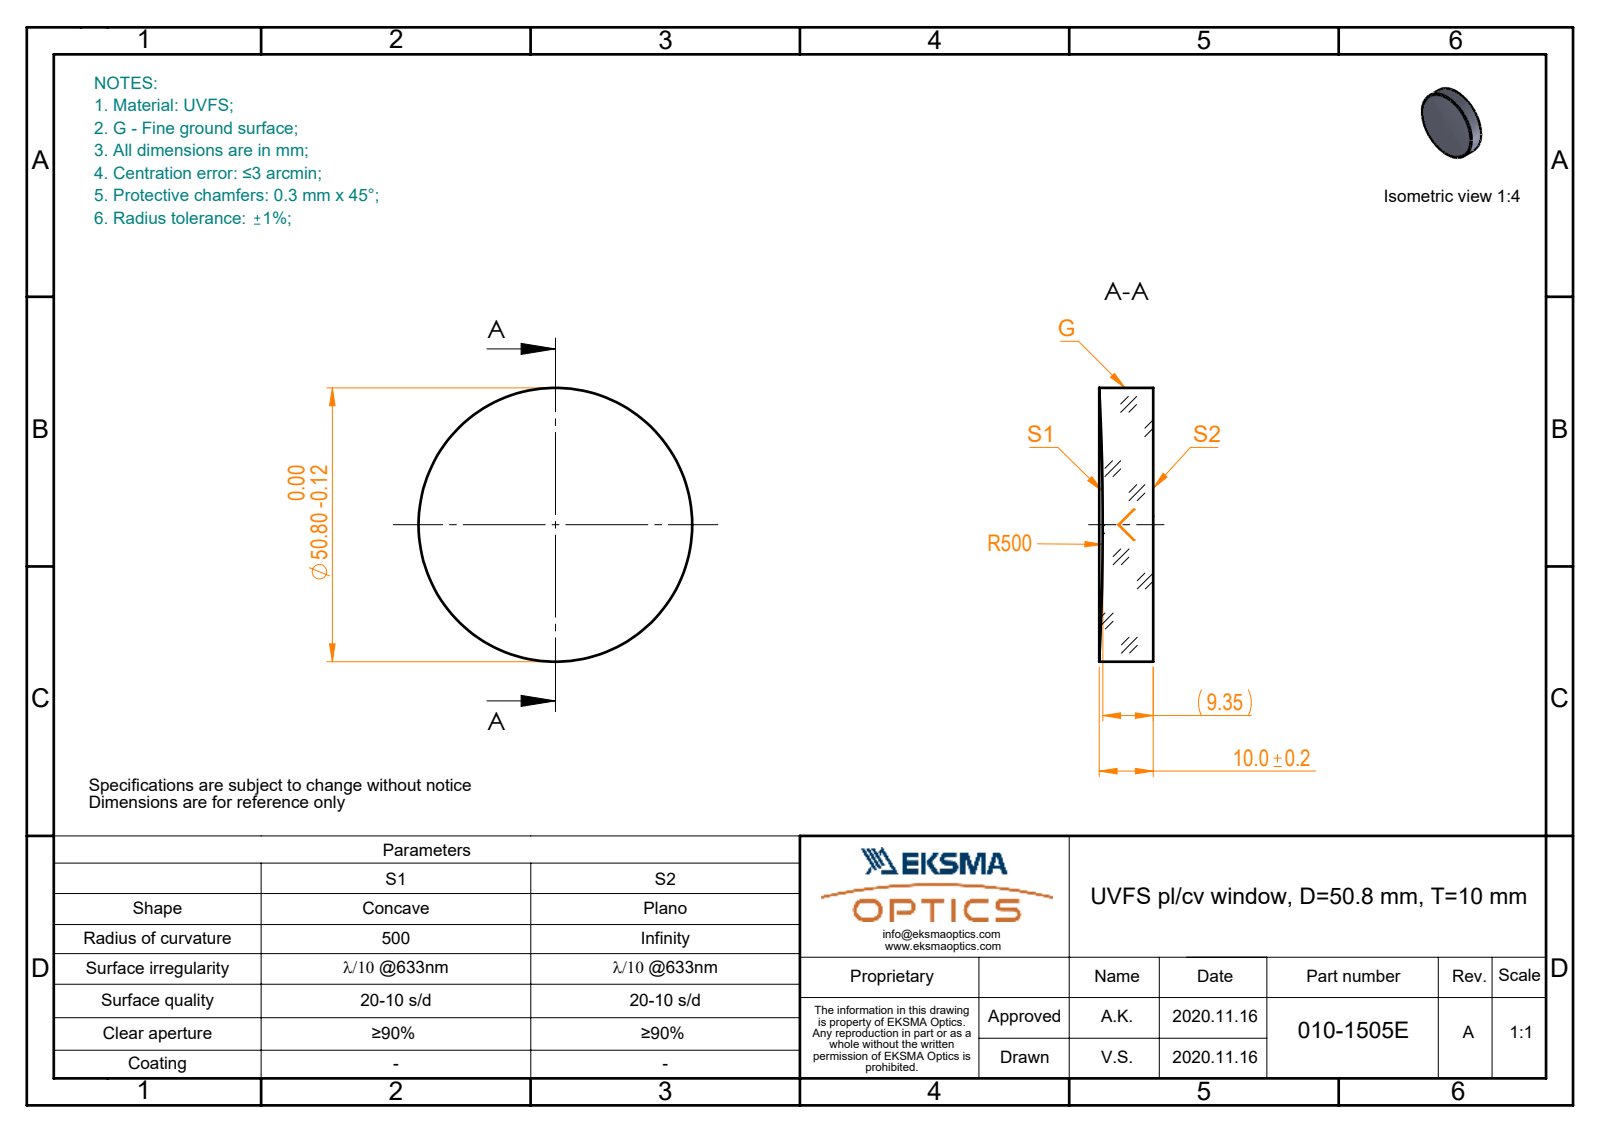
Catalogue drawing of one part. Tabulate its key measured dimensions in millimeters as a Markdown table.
| quantity | value |
| --- | --- |
| part name | 010-1505E_UVFS_PCV_window |
| STEP written by | SolidWorks 2019 (CONFIG_CONTROL_DESIGN) |
| units | millimeters |
| bodies | 1 solid, 5 faces (1 planar, 2 cylindrical, 2 other) |
| overall size | 50.8 × 50.8 × 10 |
| volume | 19 614 mm³ |
| surface area | 5 651 mm² |
| round bosses / shafts (diameter × count) | 50.8 × 1 |
